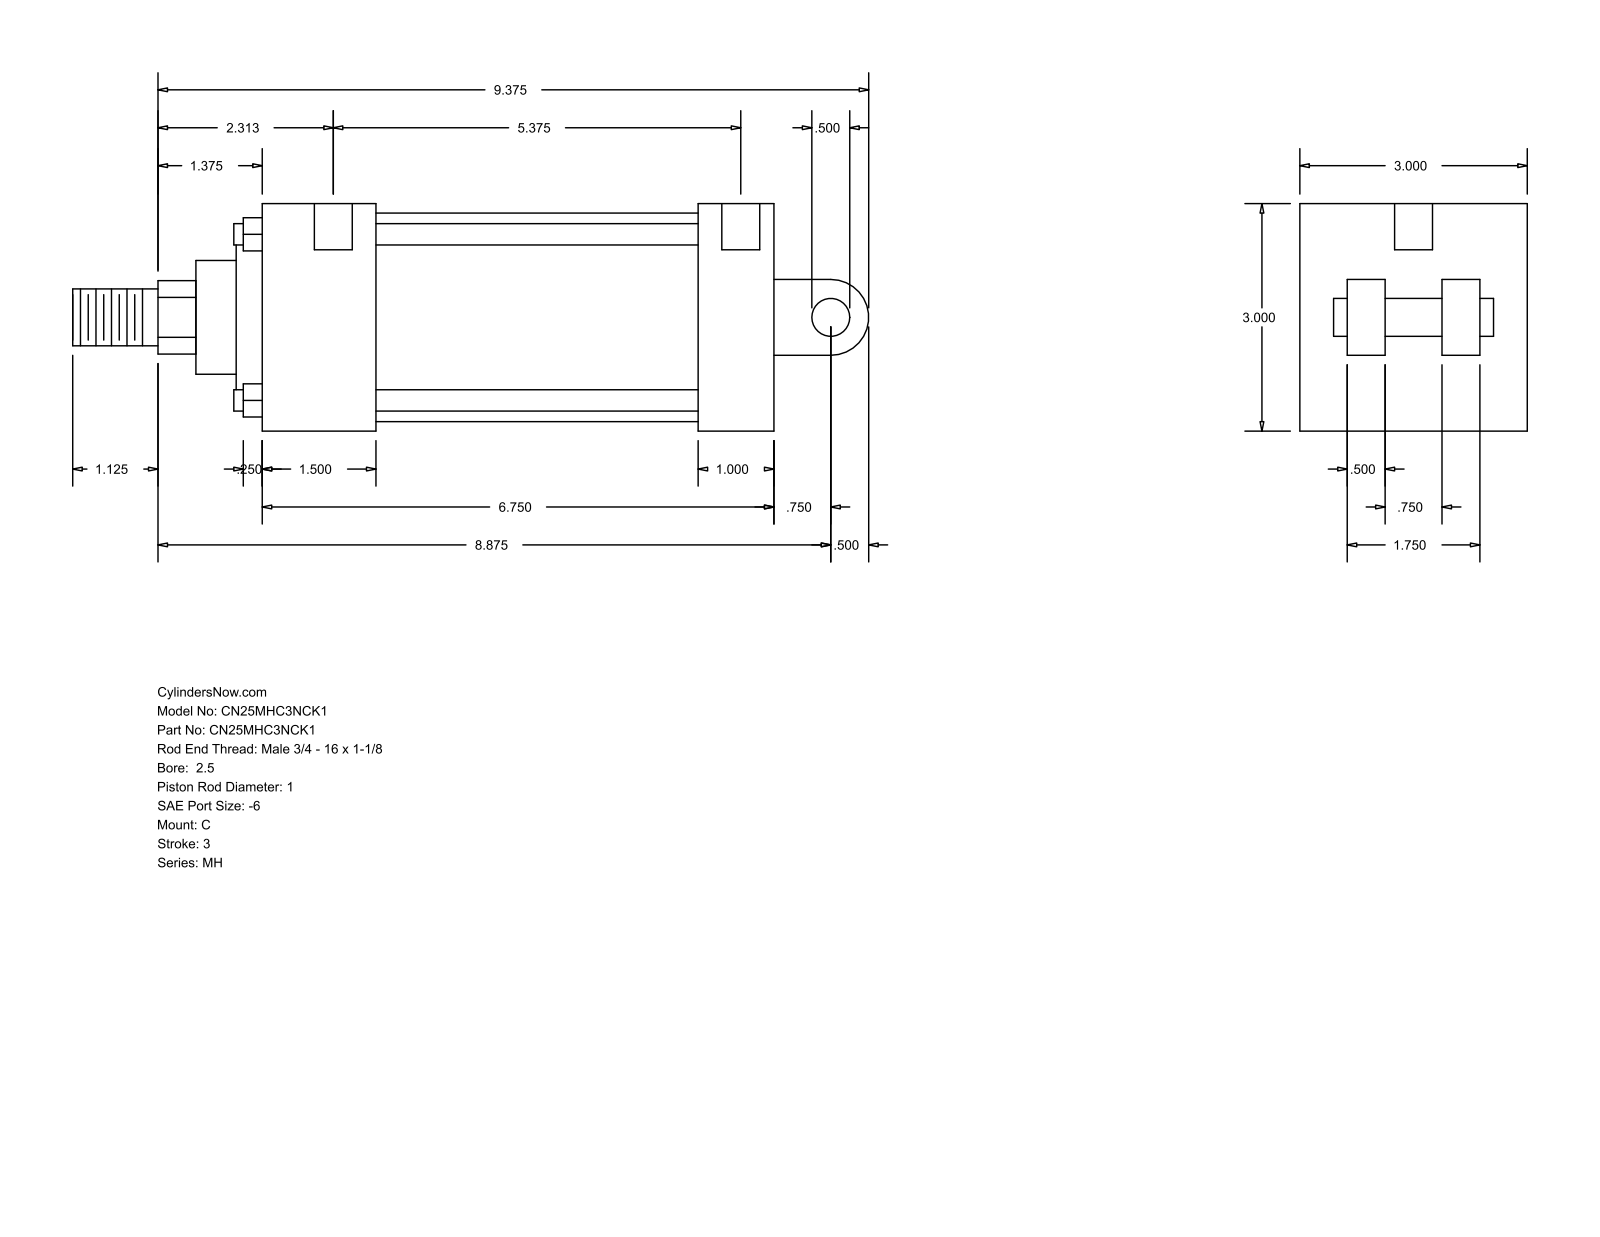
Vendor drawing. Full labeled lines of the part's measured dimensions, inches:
Part name (STEP PRODUCT): MH_C__0250_1
STEP written by: GSSL Pune (CONFIG_CONTROL_DESIGN)
Units: inches
Bodies: 0 solids, 101 faces (71 planar, 30 cylindrical, 0 other)
Overall size (bounding box): 10.5 × 3 × 3
Round holes (diameter × count): ⌀0.219 ×4, ⌀0.5 ×2
Round bosses / shafts (diameter × count): ⌀0.281 ×4, ⌀2.75 ×1, ⌀2.375 ×1, ⌀1.5 ×1, ⌀1 ×1, ⌀0.75 ×1, ⌀0.5 ×1
Partial cylindrical surfaces — rounded edges, fillets, slot ends (radius × count): R0.484 ×1, R0.5 ×1
Main face-to-face distances: 3, 6.75, 2.375, 0.625, 5.75, 1, 1.5, 4.25, 5.25, 0.5
Hole centre spacings: 5.687, 0.125, 0.187, 5.375, 5.5, 5.562
